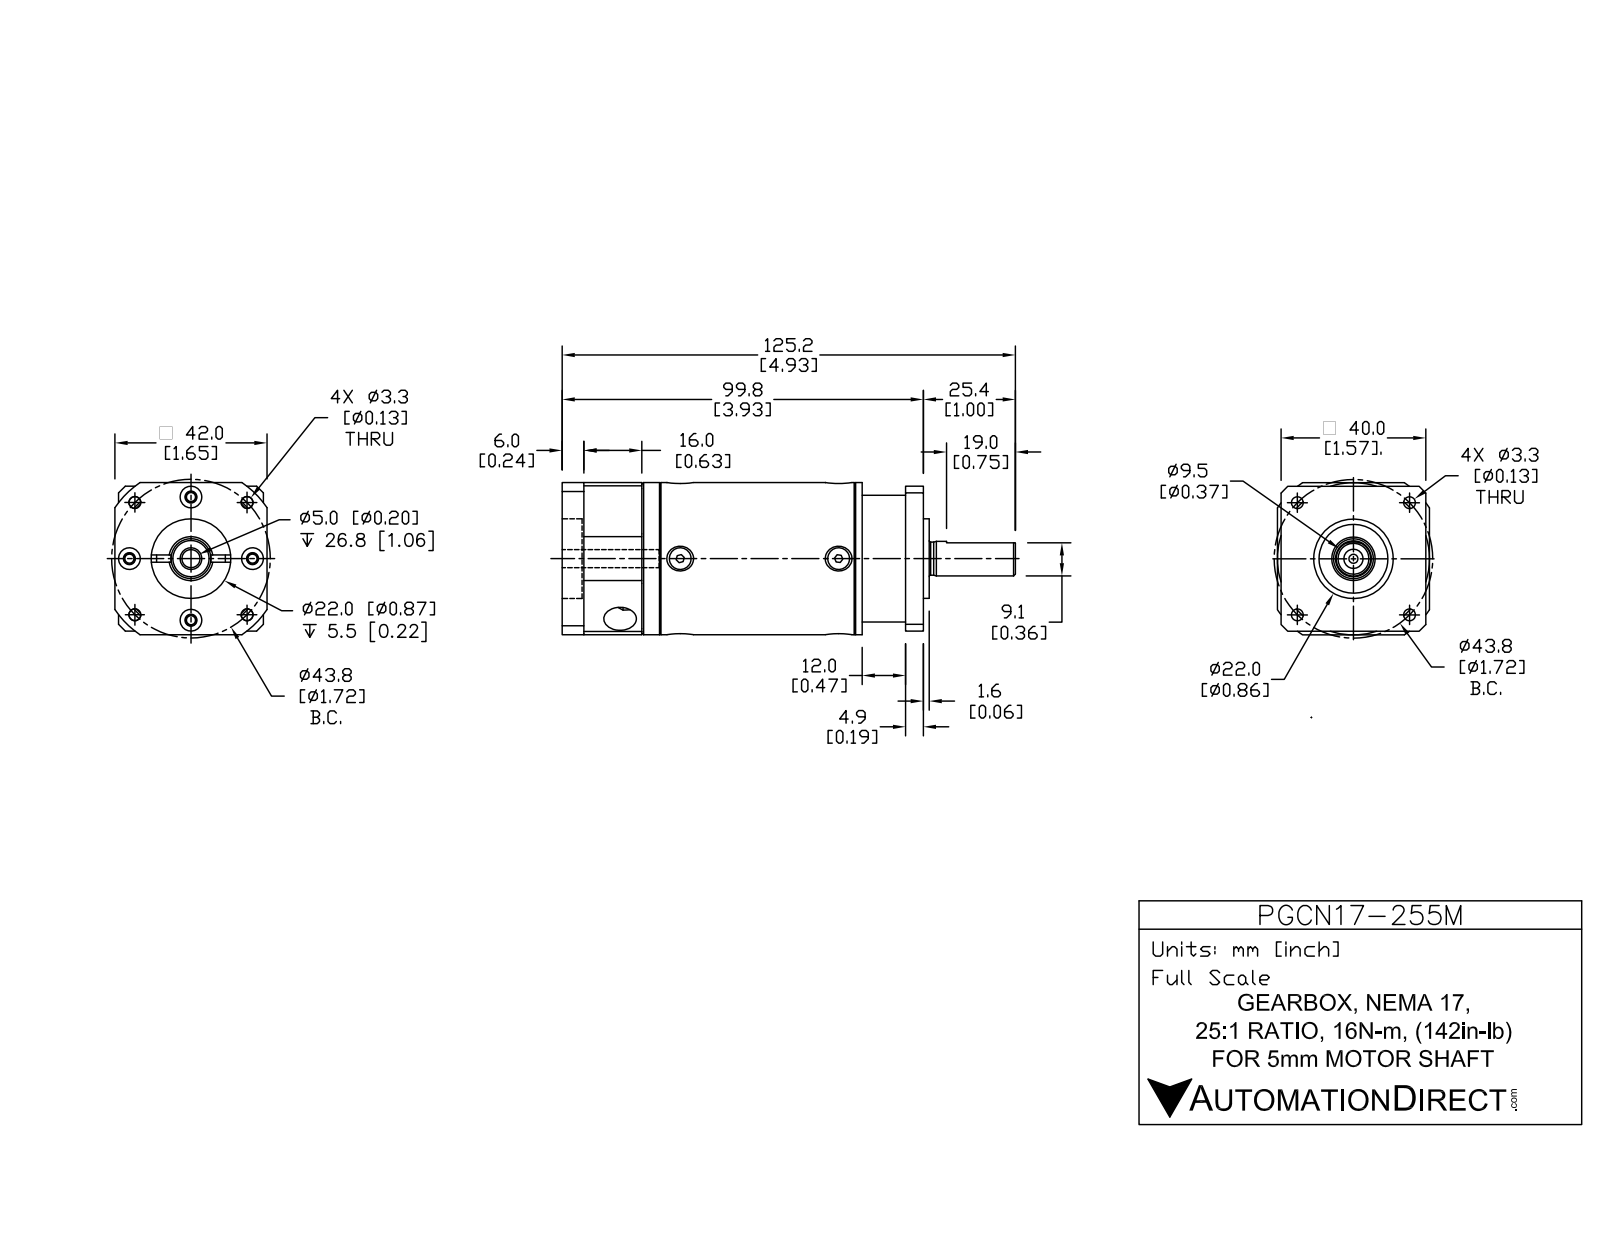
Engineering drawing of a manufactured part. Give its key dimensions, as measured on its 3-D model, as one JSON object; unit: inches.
{"part_name": "PGCN17-255M; N17-E05_1; PE-N17-II 11mm Input; Bushing_5x11x14.9_1", "step_written_by": "SolidWorks 2014 (AUTOMOTIVE_DESIGN)", "units": "inches", "bodies": {"solids": 3, "faces": 433, "planar": 137, "cylindrical": 174, "other": 122}, "overall_size": [4.927, 1.654, 1.654], "volume_in3": 7.555, "surface_area_in2": 45.37, "round_holes": [[0.13, 8], [0.098, 5], [0.118, 4], [0.128, 4], [0.134, 4], [0.236, 4], [0.177, 2], [0.354, 2], [0.197, 1], [0.433, 1], [0.748, 1], [0.866, 1]], "round_bosses_or_shafts": [[0.236, 4], [0.276, 2], [0.157, 2], [1.654, 1], [1.378, 1], [0.865, 1], [0.472, 1], [0.375, 1]], "partial_cylinders_radius": [[0.064, 2], [0.157, 2], [0.748, 1], [1.063, 1], [1.102, 1]], "face_to_face_distances": [0.866, 3.061, 3.927, 0.039, 1.614, 0.193, 2.868, 3.734, 1.457, 0.63], "hole_center_spacings": [0.613, 0.613, 1.22, 1.417, 1.418, 0.669, 0.863, 0.863]}
